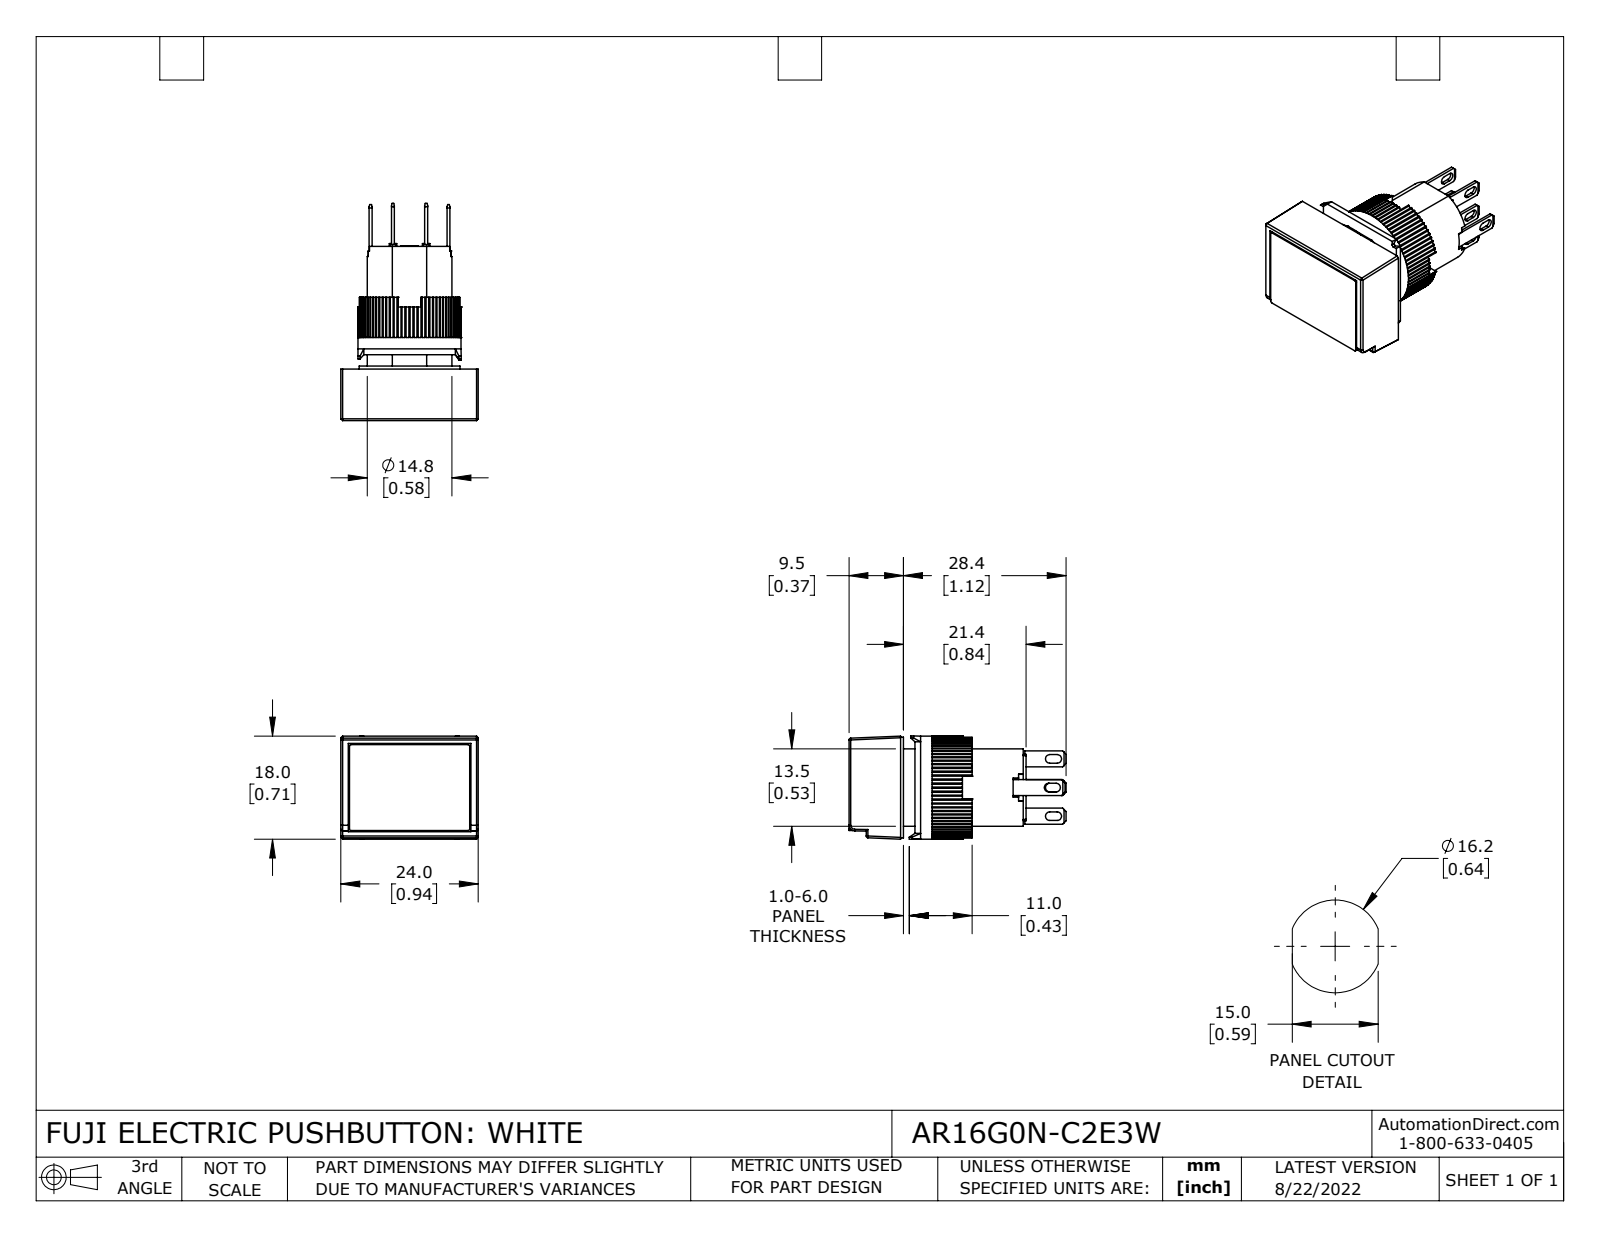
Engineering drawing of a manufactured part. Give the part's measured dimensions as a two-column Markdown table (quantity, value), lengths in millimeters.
| quantity | value |
| --- | --- |
| part name | AR16G0N-C2E3W |
| STEP written by | SolidWorks 2021 (CONFIG_CONTROL_DESIGN) |
| units | millimeters |
| bodies | 14 solids, 841 faces (654 planar, 181 cylindrical, 6 other) |
| overall size | 37.9 × 24 × 18 |
| volume | 7 340 mm³ |
| surface area | 6 131 mm² |
| round holes (diameter × count) | 13.8 × 1, 14.8 × 1 |
| round bosses / shafts (diameter × count) | 18 × 1, 17.6 × 1 |
| partial cylindrical surfaces (radius × count) | 0.3 × 80, 0.2 × 12, 0.8 × 8, 0.3 × 6, 1 × 1 |
| main face-to-face distances | 5.4, 9, 3.6, 8.9, 12.5, 3.5, 0.5, 21.4, 1.5, 11.5 |
